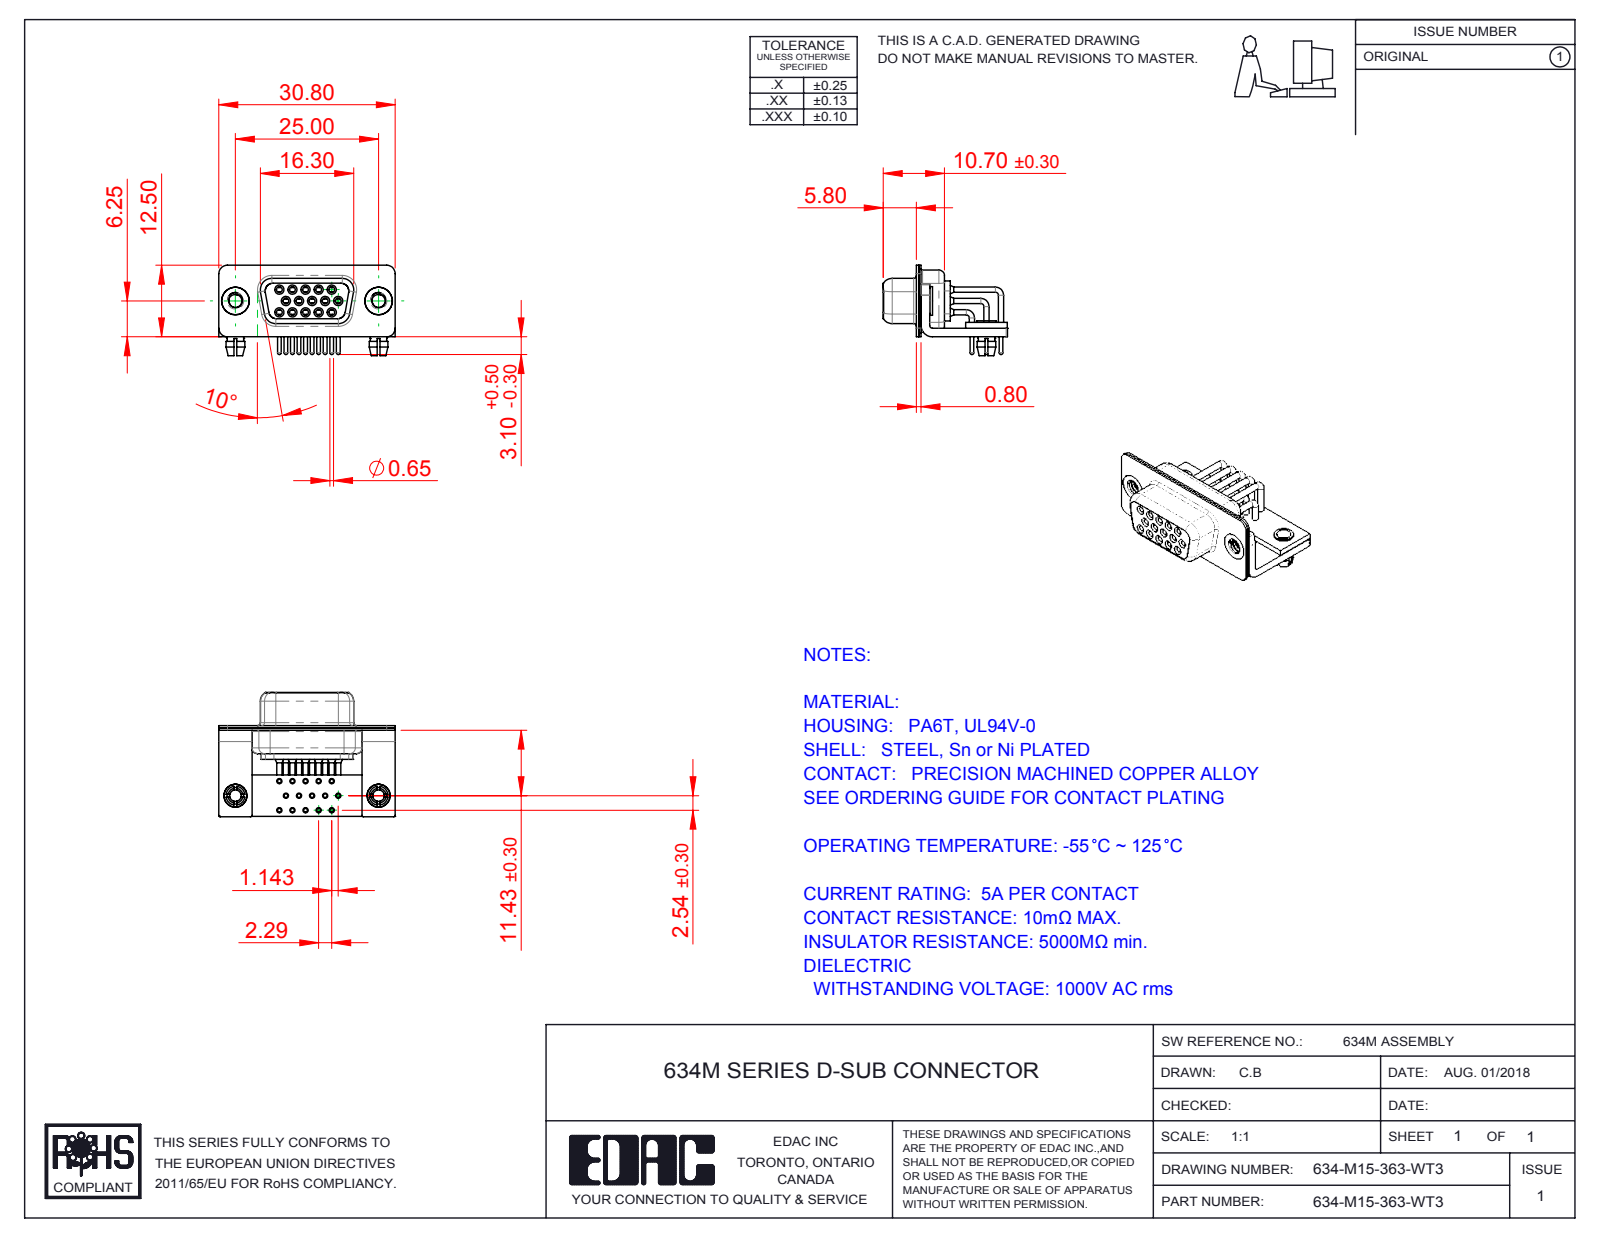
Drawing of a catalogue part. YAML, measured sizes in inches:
part_name: "634M Stabilizer Bracket; 634M Contact Row 2; 634M Housing_15 Contacts; 634M Contact Row 3 (+7 more)"
step_written_by: "SolidWorks 2016 (CONFIG_CONTROL_DESIGN)"
units: inches
bodies: {solids: 25, faces: 1246, planar: 366, cylindrical: 566, other: 314}
overall_size: [1.213, 0.854, 0.622]
volume: 0.138
surface_area: 10.94
round_holes:
  - {diameter: 0.079, count: 17}
  - {diameter: 0.035, count: 15}
  - {diameter: 0.039, count: 15}
  - {diameter: 0.043, count: 15}
  - {diameter: 0.067, count: 15}
  - {diameter: 0.071, count: 15}
  - {diameter: 0.089, count: 2}
  - {diameter: 0.098, count: 2}
  - {diameter: 0.126, count: 2}
  - {diameter: 0.157, count: 2}
  - {diameter: 0.189, count: 2}
round_bosses_or_shafts:
  - {diameter: 0.063, count: 15}
  - {diameter: 0.059, count: 15}
  - {diameter: 0.035, count: 15}
  - {diameter: 0.026, count: 15}
  - {diameter: 0.197, count: 2}
  - {diameter: 0.193, count: 2}
  - {diameter: 0.157, count: 2}
  - {diameter: 0.134, count: 2}
partial_cylinders:
  - {radius: 0.01, count: 16}
  - {radius: 0.059, count: 16}
  - {radius: 0.079, count: 13}
  - {radius: 0.053, count: 8}
  - {radius: 0.063, count: 8}
  - {radius: 0.02, count: 5}
  - {radius: 0.024, count: 4}
  - {radius: 0.026, count: 4}
face_to_face_distances: [0.016, 0.059, 0.031, 0.039, 0.091, 0.075, 0.368, 0.098, 0.057, 0.352]
hole_center_spacings: [0.09, 0.09, 0.18, 0.156, 0.168, 0.109, 0.238, 0.27]
